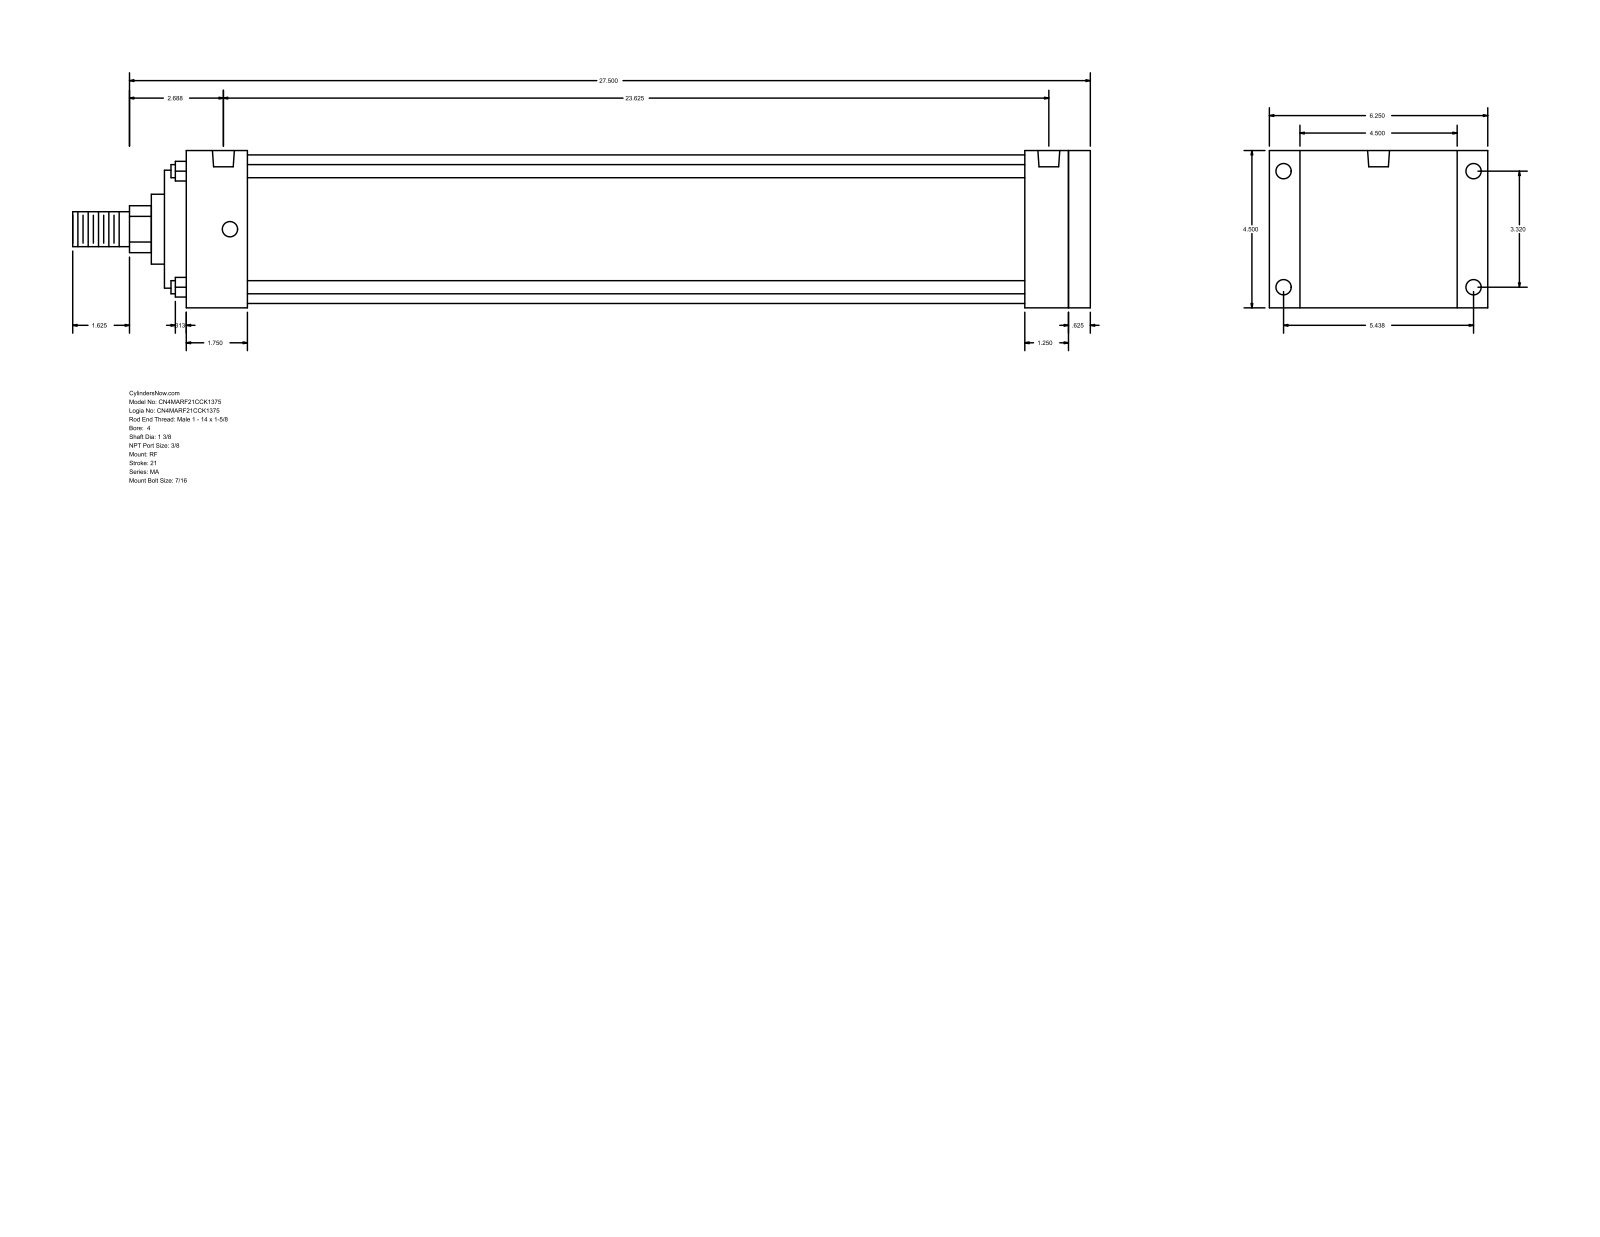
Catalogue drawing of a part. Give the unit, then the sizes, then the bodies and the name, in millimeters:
Units: millimetres
Overall size (bounding box): 739.77 × 158.75 × 114.3
Round holes (diameter × count): ⌀11.11 ×8, ⌀15.93 ×2
Round bosses / shafts (diameter × count): ⌀9.53 ×4, ⌀107.95 ×1, ⌀85.72 ×1, ⌀50.8 ×1, ⌀34.92 ×1, ⌀25.4 ×1
Partial cylindrical surfaces — rounded edges, fillets, slot ends (radius × count): R17.06 ×1
Main face-to-face distances: 114.3, 657.23, 15.88, 641.35, 15.87, 657.22, 673.1, 22.23, 136.53, 625.48
Hole centre spacings: 84.32, 138.12, 161.82, 590.55, 4.76, 4.77, 595.31, 595.32
Bodies: 0 solids, 94 faces (65 planar, 29 cylindrical, 0 other)
Part name (STEP PRODUCT): MA_RF__0400_1.375
STEP written by: GSSL Pune (CONFIG_CONTROL_DESIGN)
